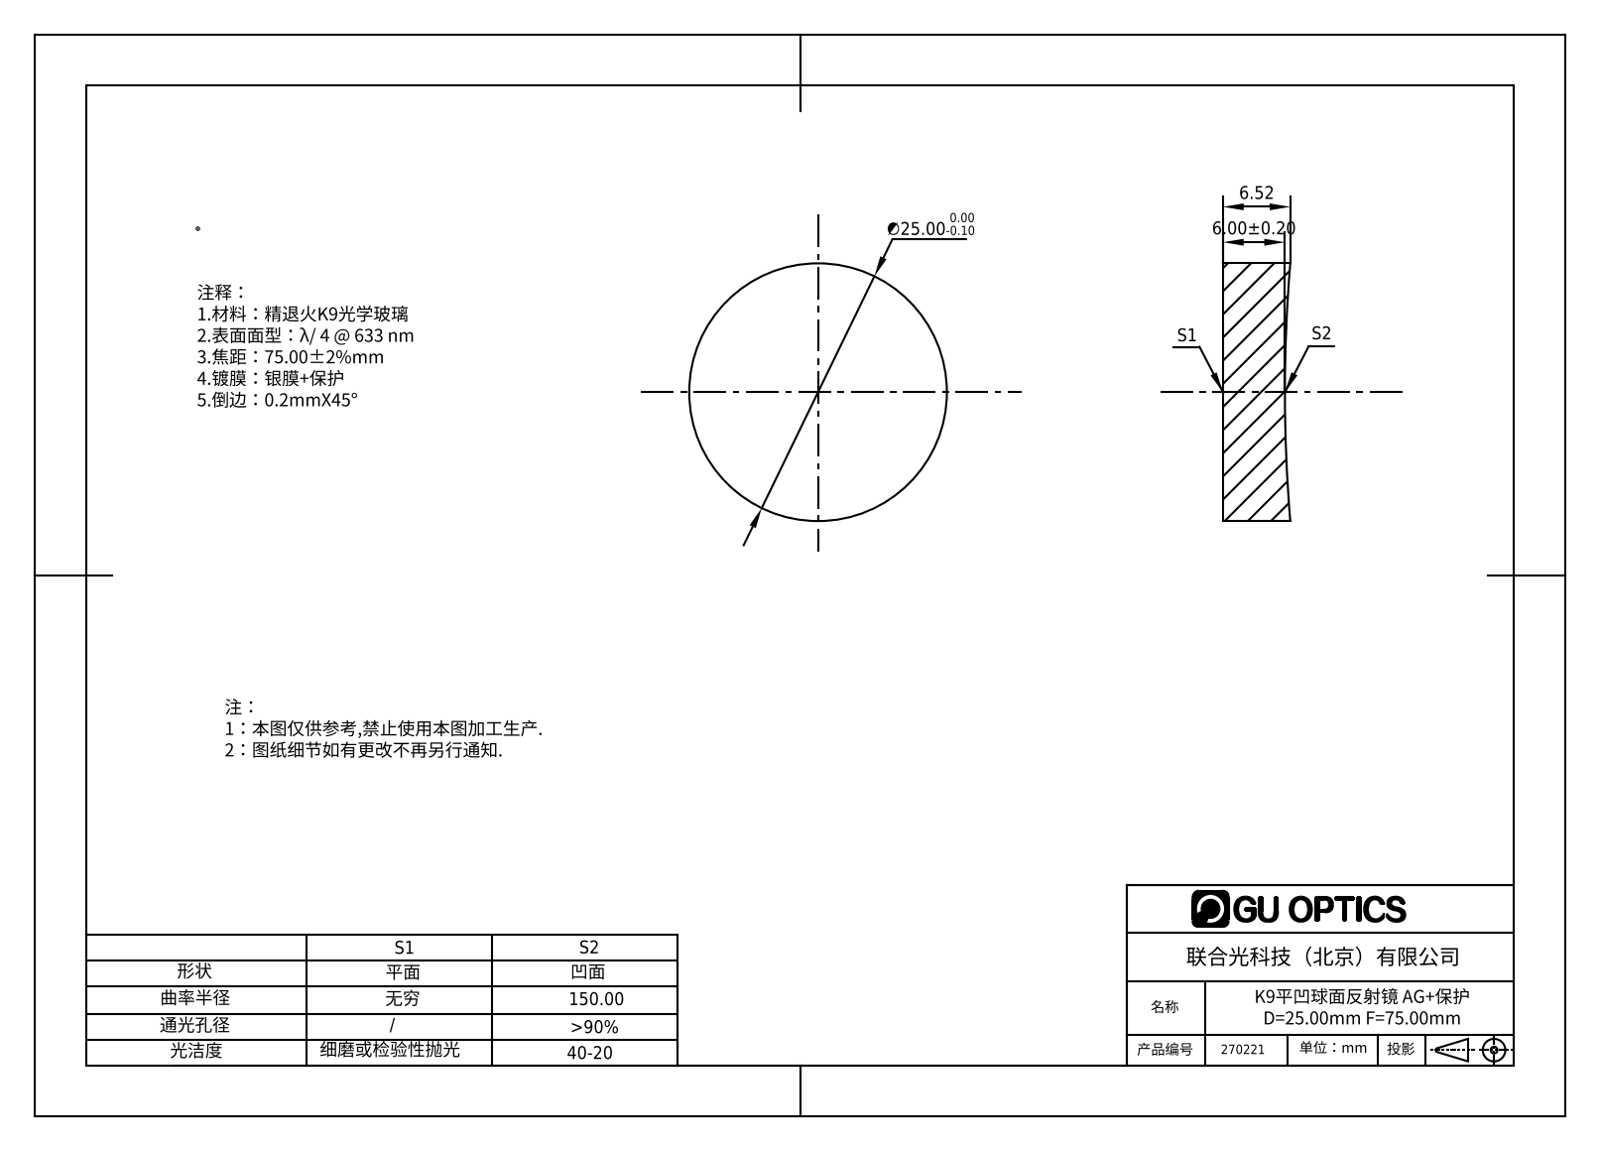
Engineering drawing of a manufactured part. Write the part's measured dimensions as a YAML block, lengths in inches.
part_name: "270026"
step_written_by: "SolidWorks 2016 (AUTOMOTIVE_DESIGN)"
units: inches
bodies: {solids: 1, faces: 5, planar: 1, cylindrical: 2, other: 2}
overall_size: [0.984, 0.984, 0.257]
volume: 0.188
surface_area: 2.317
round_bosses_or_shafts:
  - {diameter: 0.984, count: 1}
